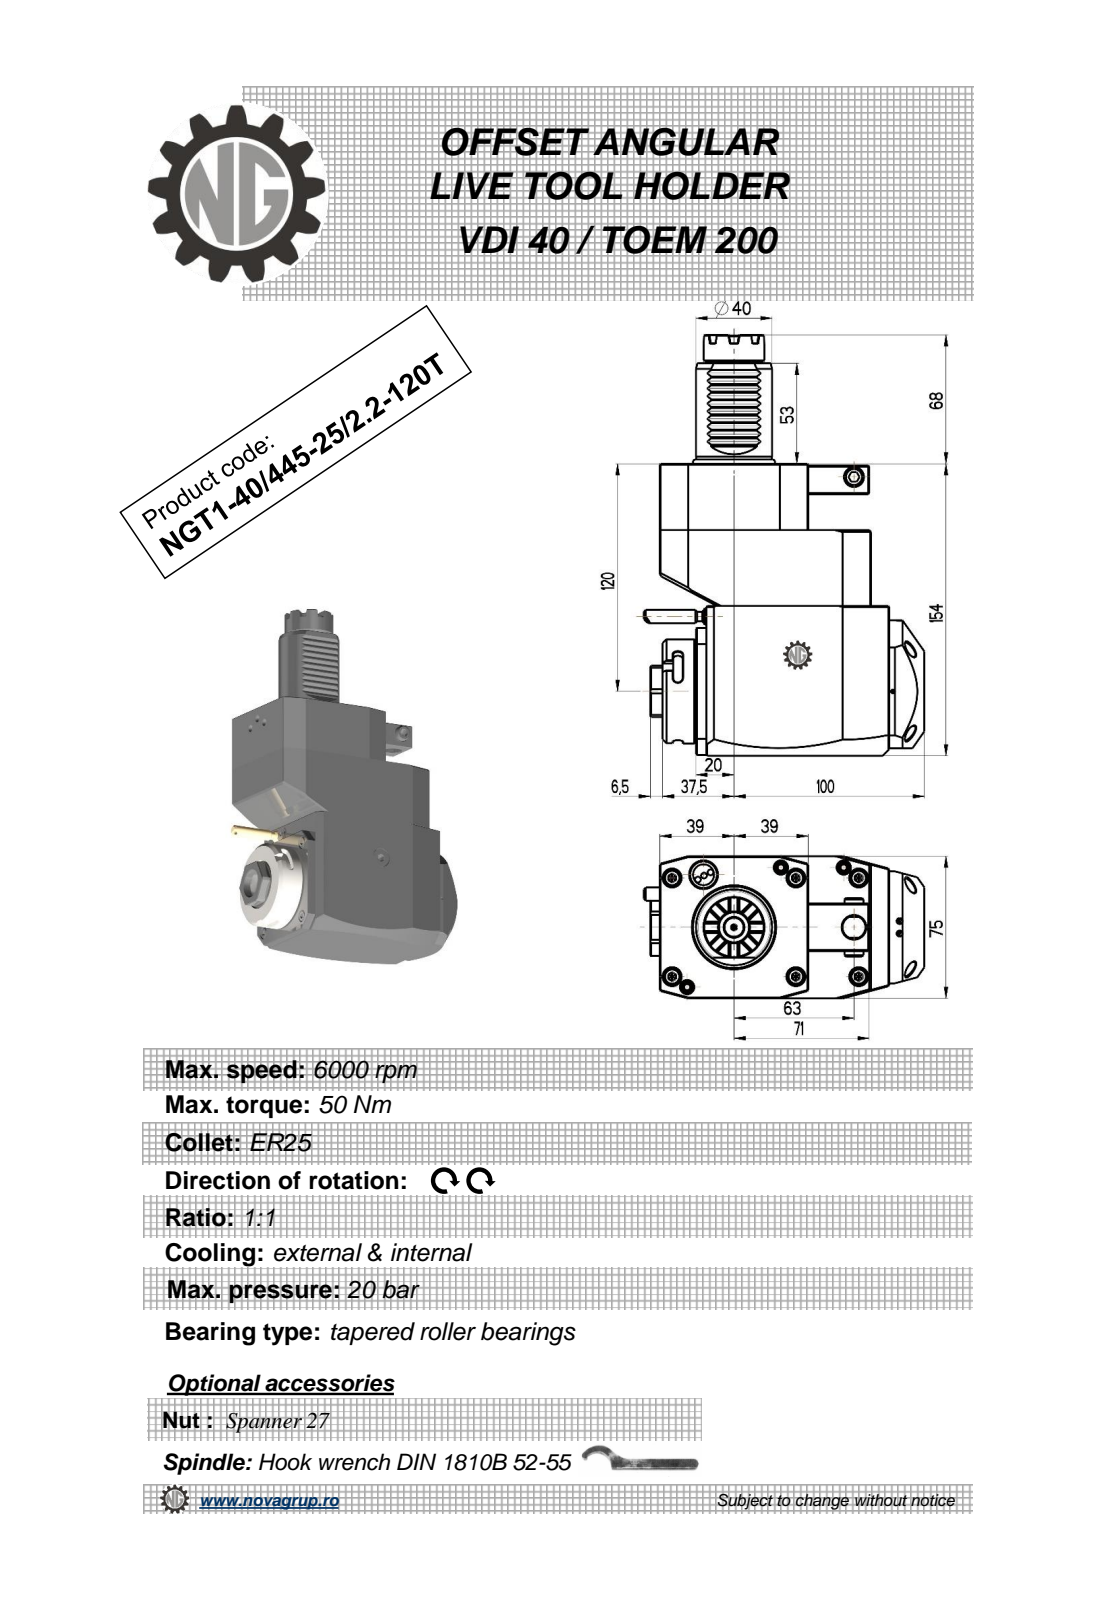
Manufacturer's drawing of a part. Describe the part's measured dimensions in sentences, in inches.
The part is named "NGT1_40_445_25_1_2_120T". Its 3-D file was written by "PRO/ENGINEER BY PARAMETRIC TECHNOLOGY CORPORATION, 2010280 (CONFIG_CONTROL_DESIGN)". It is 1 solid with 411 faces: 225 planar, 78 cylindrical and 108 other. Overall it measures 8.74 by 5.8 by 2.953 inches. Its volume is 77.26 cubic inches and its surface area 138.8 square inches. Round holes: 1 of diameter 0.098, 1 of diameter 0.118, 1 of diameter 0.335, 1 of diameter 0.374, 1 of diameter 0.472, 1 of diameter 0.709. Round bosses or shafts: 2 of diameter 0.353, 1 of diameter 2.165, 1 of diameter 1.89, 1 of diameter 1.575, 1 of diameter 1.26, 1 of diameter 0.661, 1 of diameter 0.394, 1 of diameter 0.276. Partial cylindrical surfaces (rounded edges, fillets, slot ends): 10 of radius 0.012, 6 of radius 0.098, 2 of radius 7.087, 1 of radius 0.02, 1 of radius 0.339, 1 of radius 0.591, 1 of radius 0.965, 1 of radius 1.476. The main face-to-face distances are 2.953, 6.063, 4.685, 0.748, 2.323, 4.37, 1.378, 3.622, 0.689, 3.071. The hole center spacings are 1.701, 2.956, 4.429.
